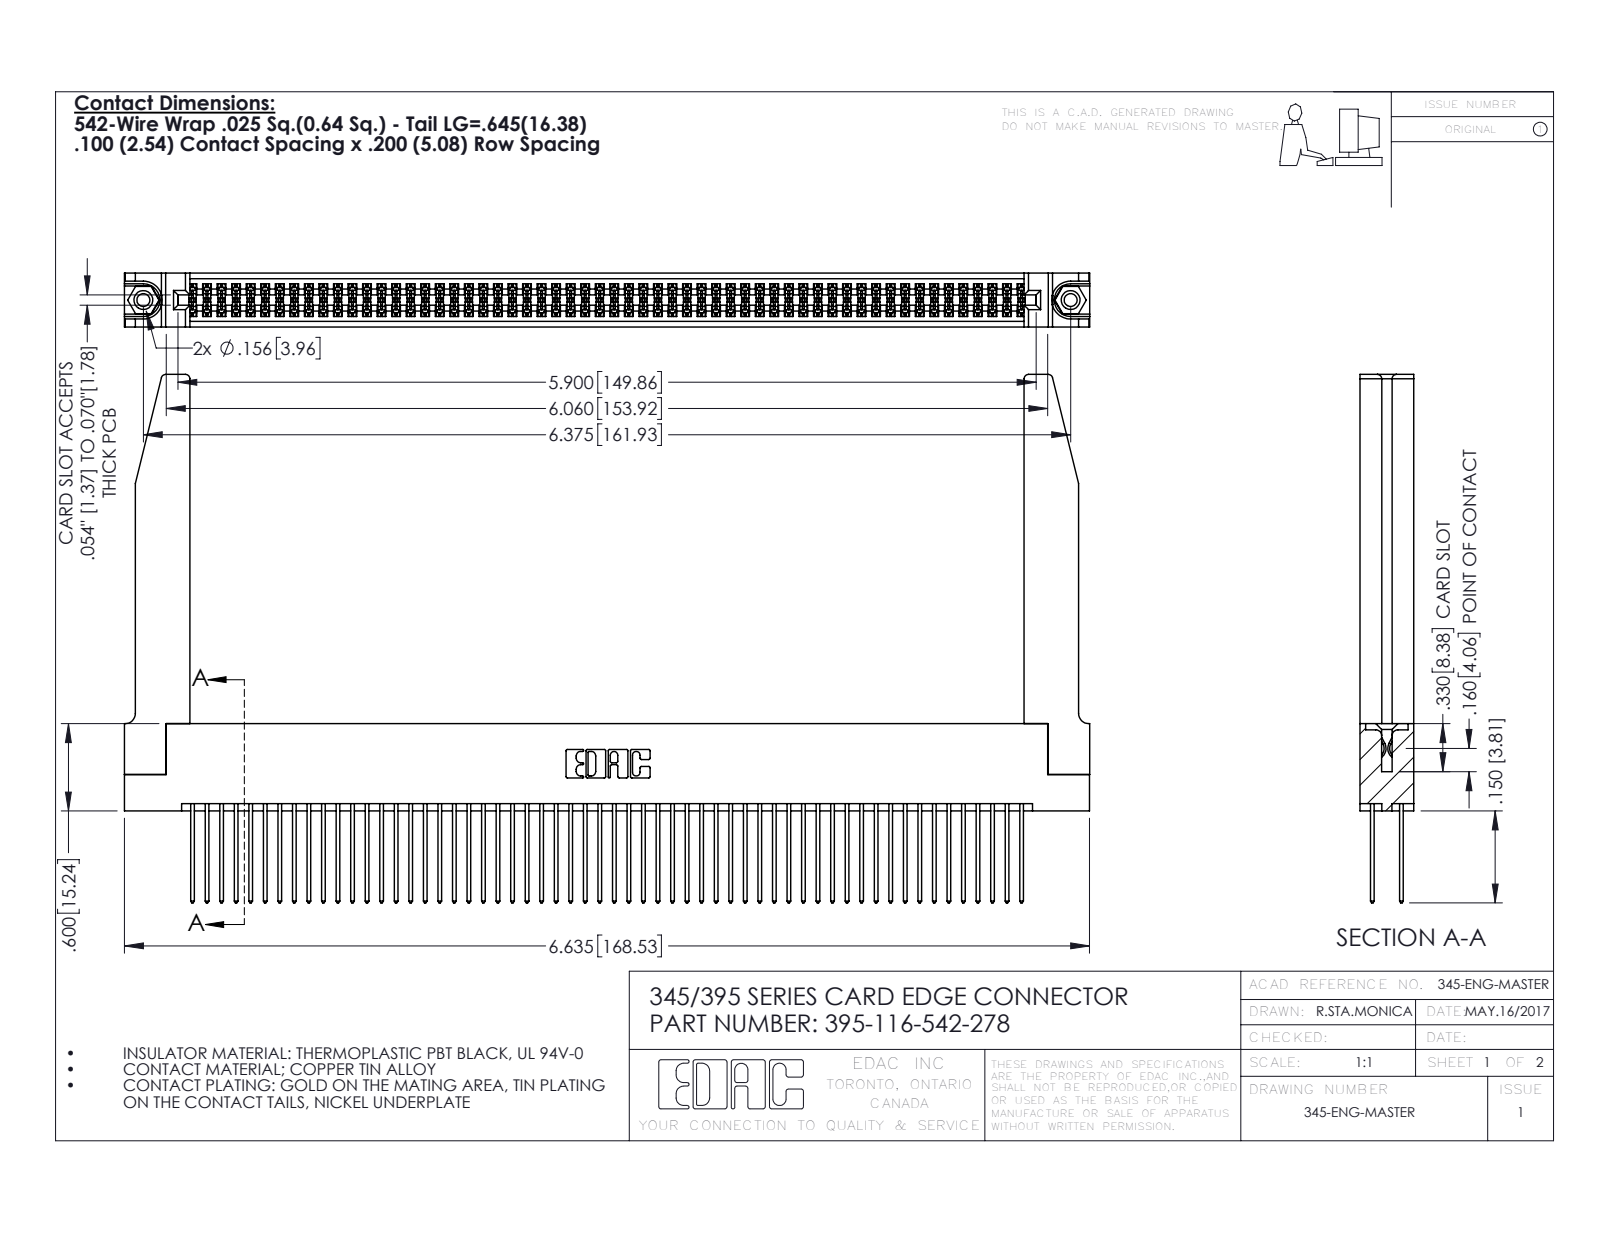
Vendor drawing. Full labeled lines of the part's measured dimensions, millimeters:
Part name (STEP PRODUCT): 345-292-001_345-293-142; 345-250-001_345-250-001-102; 395-116-542-278; 345 Part_Flush Mounting Lugs - 0.156 Dia-TH (+1 more)
STEP written by: SolidWorks 2016 (CONFIG_CONTROL_DESIGN)
Units: millimetres
Bodies: 121 solids, 6160 faces (4050 planar, 2058 cylindrical, 52 other)
Overall size (bounding box): 168.6 × 92.3 × 9.4
Volume: 24 830 mm³ · Surface area: 34 900 mm²
Round holes (diameter × count): ⌀2.3 ×2, ⌀3.2 ×2, ⌀4 ×2, ⌀1.6 ×1
Round bosses / shafts (diameter × count): ⌀3.9 ×2
Partial cylindrical surfaces — rounded edges, fillets, slot ends (radius × count): R0.2 ×174, R0.3 ×116, R0.3 ×22, R0.8 ×8, R0.2 ×6, R0.8 ×6, R0.7 ×3, R0.4 ×2
Main face-to-face distances: 1.8, 7.6, 9.4, 5.1, 2.5, 6.9, 0.6, 5.7, 4.4, 3.8
Hole centre spacings: 6.9, 155.9, 161.9
